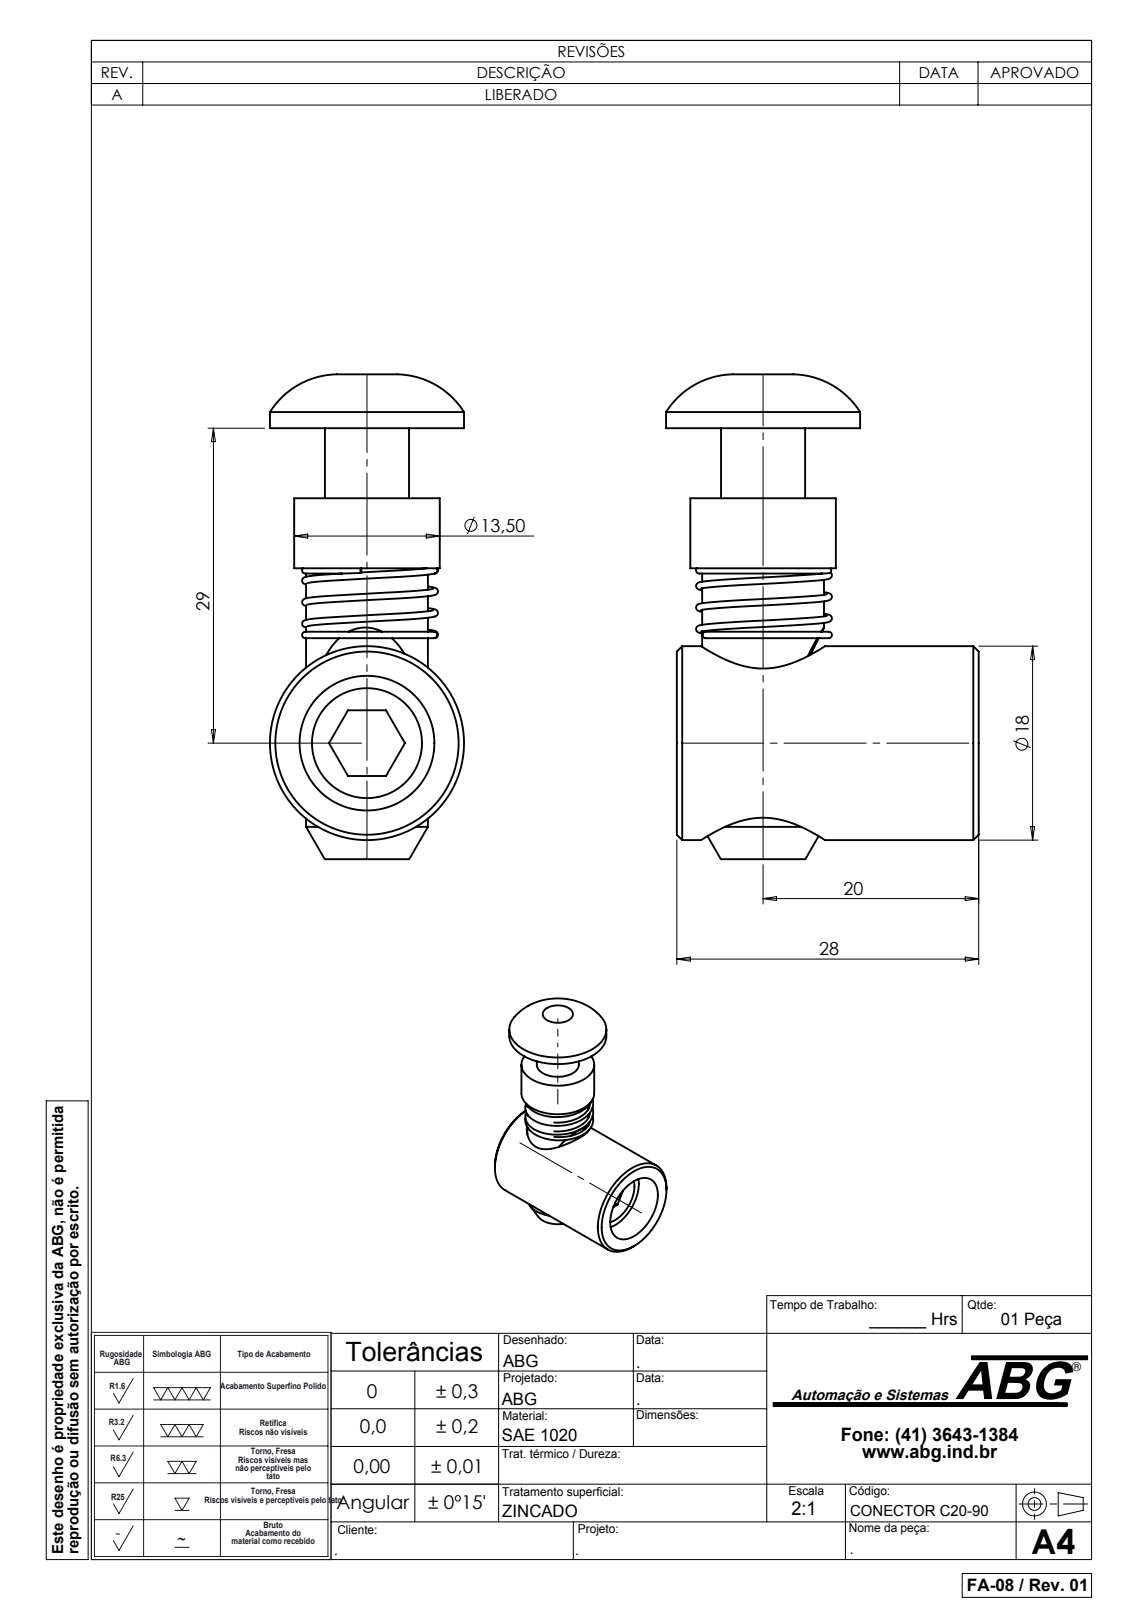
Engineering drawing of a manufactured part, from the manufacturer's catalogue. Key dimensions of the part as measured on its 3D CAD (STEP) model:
Part name (STEP PRODUCT): C20-90; BUCHA 220-20; PINO UNIVERSAL 222-90-25; MOLA 225-10 (+1 more)
STEP written by: SolidWorks 2007 (CONFIG_CONTROL_DESIGN)
Units: millimetres
Bodies: 4 solids, 63 faces (21 planar, 18 cylindrical, 24 other)
Overall size (bounding box): 45 × 29 × 18
Volume: 9 295 mm³ · Surface area: 5 943 mm²
Round holes (diameter × count): ⌀10.2 ×1, ⌀11.5 ×1, ⌀12.5 ×1
Round bosses / shafts (diameter × count): ⌀18 ×2, ⌀13.5 ×1, ⌀12 ×1, ⌀11.3 ×1, ⌀7.8 ×1
Main face-to-face distances: 6.5, 28, 21.89, 6.11, 5, 6.1, 33.5, 40, 27, 13
